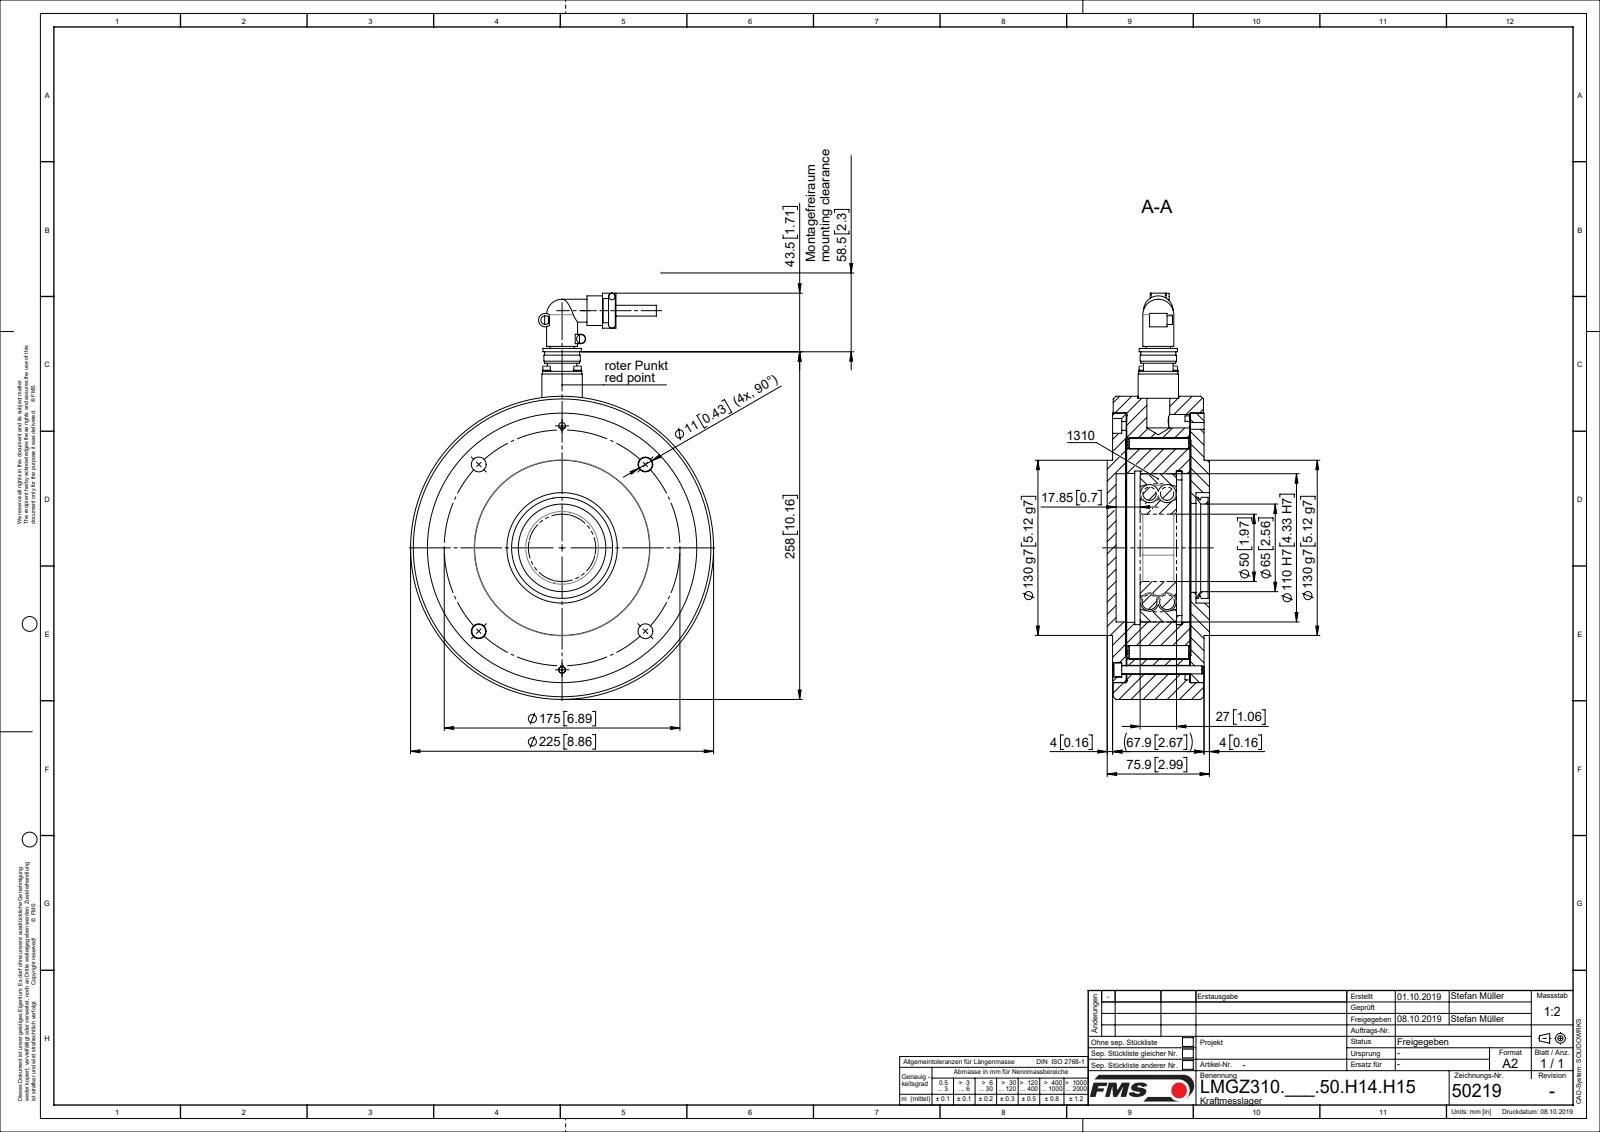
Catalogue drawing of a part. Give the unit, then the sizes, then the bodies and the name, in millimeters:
Units: millimetres
Overall size (bounding box): 301.5 × 225 × 75.9
Round holes (diameter × count): ⌀11 ×6, ⌀2.6 ×4, ⌀3.2 ×4, ⌀3.4 ×4, ⌀3.5 ×4, ⌀9 ×4, ⌀5 ×2, ⌀6.6 ×2, ⌀23 ×1, ⌀50 ×1, ⌀64 ×1, ⌀66 ×1
Round bosses / shafts (diameter × count): ⌀6.2 ×4, ⌀5.5 ×4, ⌀3 ×4, ⌀22 ×2, ⌀6.5 ×2, ⌀4.8 ×2, ⌀225 ×1, ⌀199 ×1
Partial cylindrical surfaces — rounded edges, fillets, slot ends (radius × count): R2.5 ×2, R3.5 ×1, R5 ×1, R81 ×1, R86 ×1
Main face-to-face distances: 9.7, 47.25, 10.45, 10.75, 47.45, 10.2, 57.45, 57.7, 47, 10
Hole centre spacings: 16.26, 23, 87.5, 32.53, 68.17, 68.18, 90.5, 123.74
Volume: 2 414 000 mm³ · Surface area: 390 564 mm²
Bodies: 19 solids, 391 faces (118 planar, 224 cylindrical, 49 other)
Part name (STEP PRODUCT): L50219; L49152; TEIL1; L49151 (+8 more)
STEP written by: Mechanical Desktop 2007 (CONFIG_CONTROL_DESIGN)
